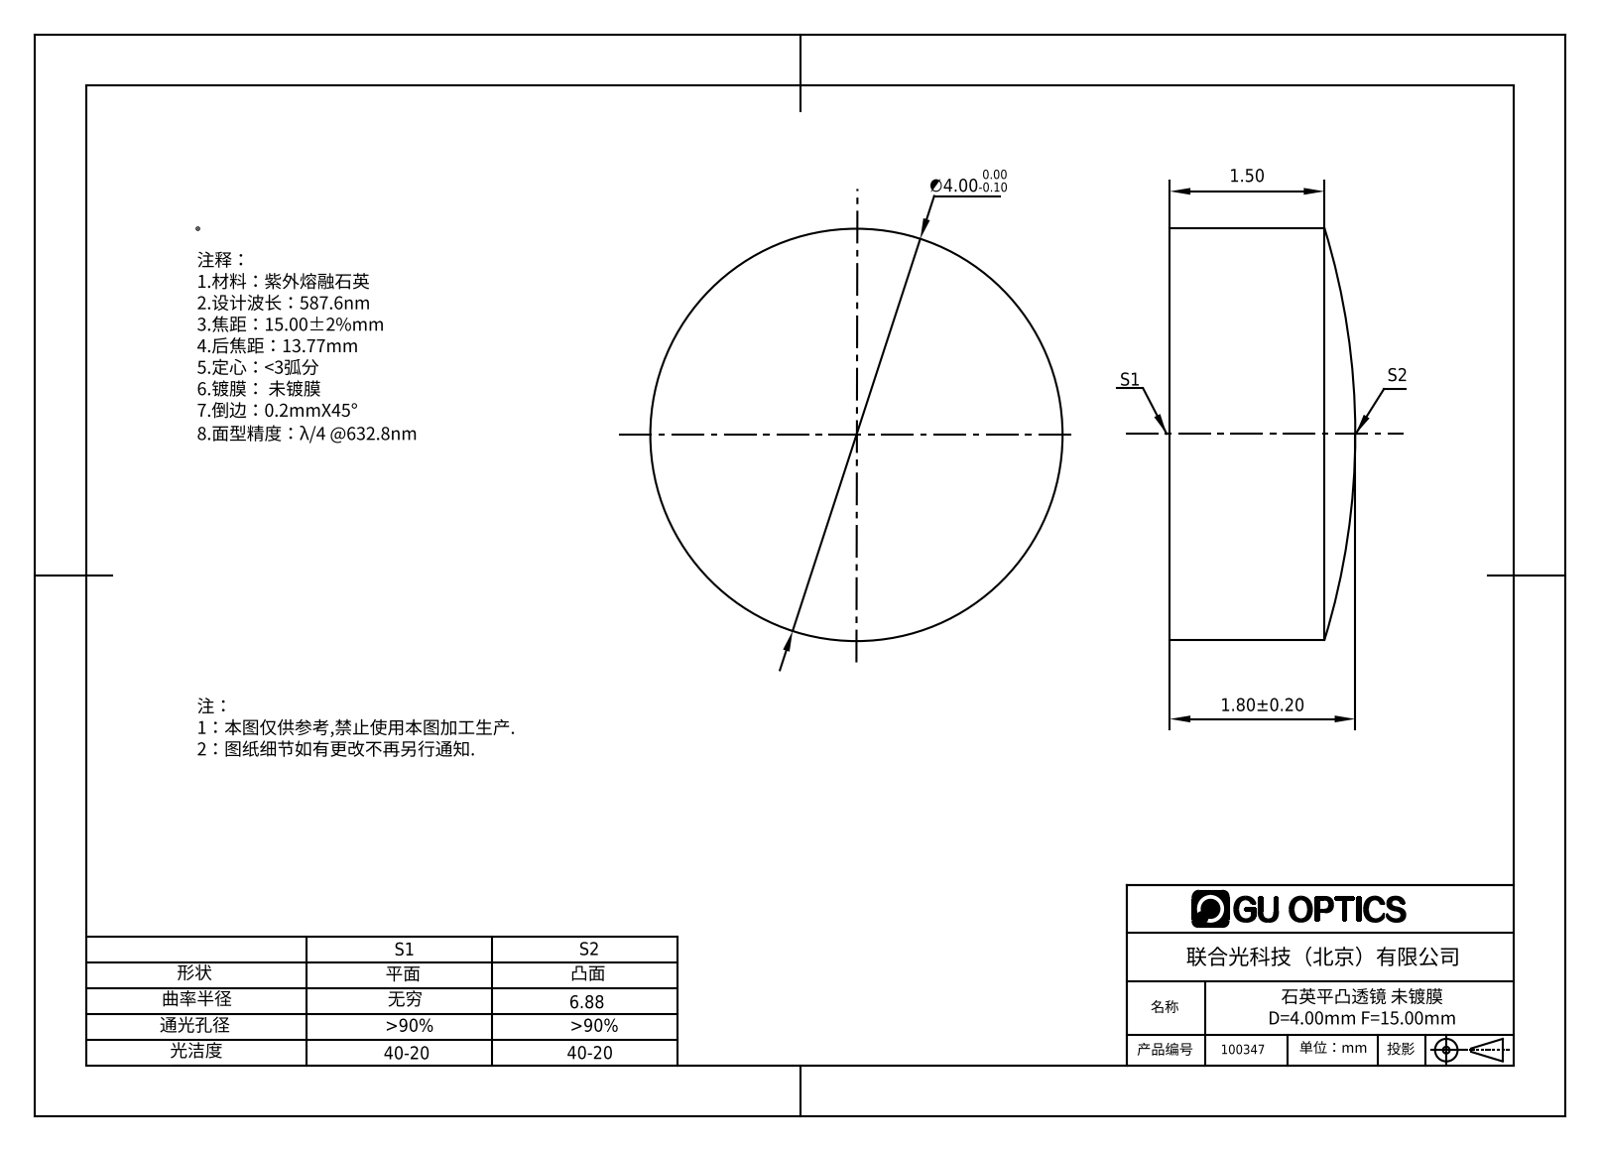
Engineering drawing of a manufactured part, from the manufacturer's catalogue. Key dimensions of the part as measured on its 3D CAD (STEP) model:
Part name (STEP PRODUCT): 100347
STEP written by: SolidWorks 2016 (AUTOMOTIVE_DESIGN)
Units: millimetres
Bodies: 1 solid, 5 faces (1 planar, 2 cylindrical, 2 other)
Overall size (bounding box): 4 × 4 × 1.8
Volume: 21 mm³ · Surface area: 44 mm²
Round bosses / shafts (diameter × count): ⌀4 ×1
